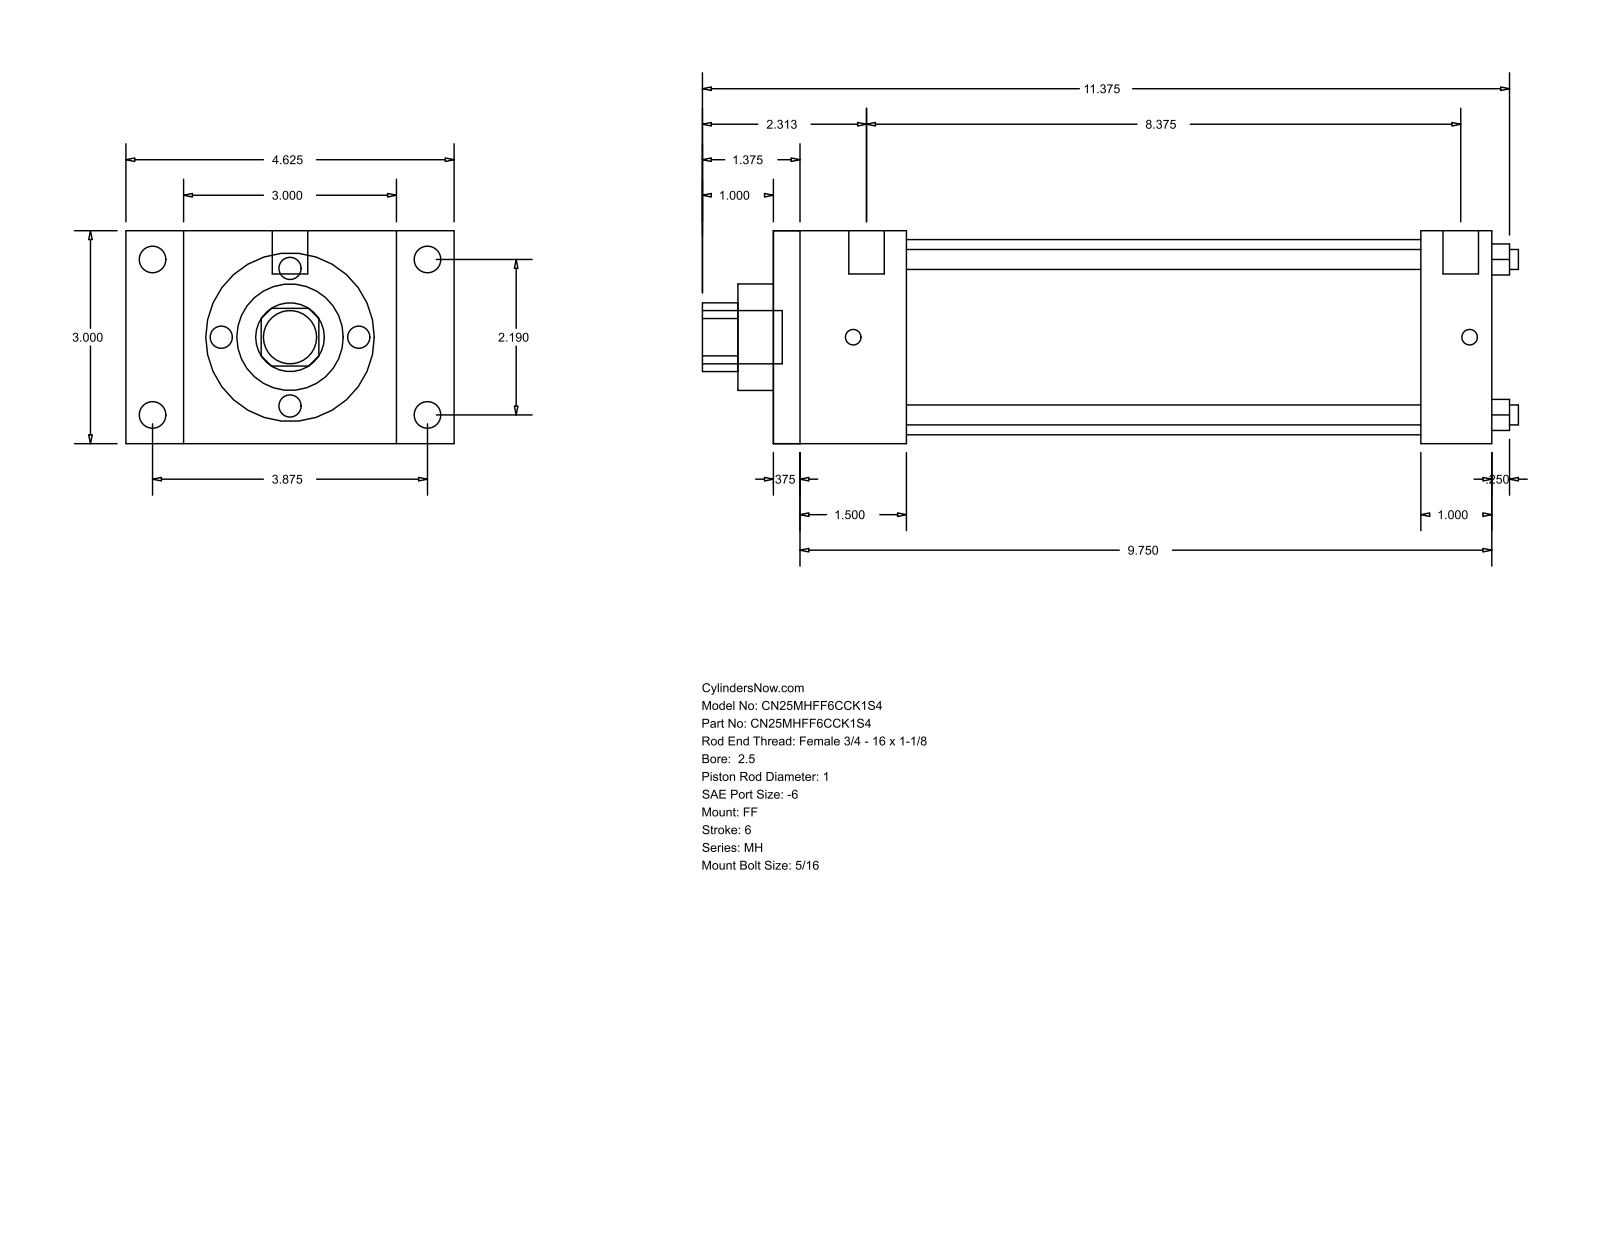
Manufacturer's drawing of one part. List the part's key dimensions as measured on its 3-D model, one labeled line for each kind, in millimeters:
Part name (STEP PRODUCT): MH_FF__0250_1
STEP written by: GSSL Pune (CONFIG_CONTROL_DESIGN)
Units: millimetres
Bodies: 0 solids, 92 faces (64 planar, 28 cylindrical, 0 other)
Overall size (bounding box): 292.1 × 117.47 × 76.2
Round holes (diameter × count): ⌀7.14 ×4, ⌀25.4 ×1, ⌀38.1 ×1, ⌀69.85 ×1
Round bosses / shafts (diameter × count): ⌀9.53 ×4, ⌀5.56 ×4, ⌀12.7 ×2, ⌀19.05 ×1
Partial cylindrical surfaces — rounded edges, fillets, slot ends (radius × count): R12.29 ×1
Main face-to-face distances: 76.2, 257.17, 247.65, 9.52, 25.39, 47.63, 231.78, 38.11, 222.26, 184.15
Hole centre spacings: 39.33, 55.62, 78.66
